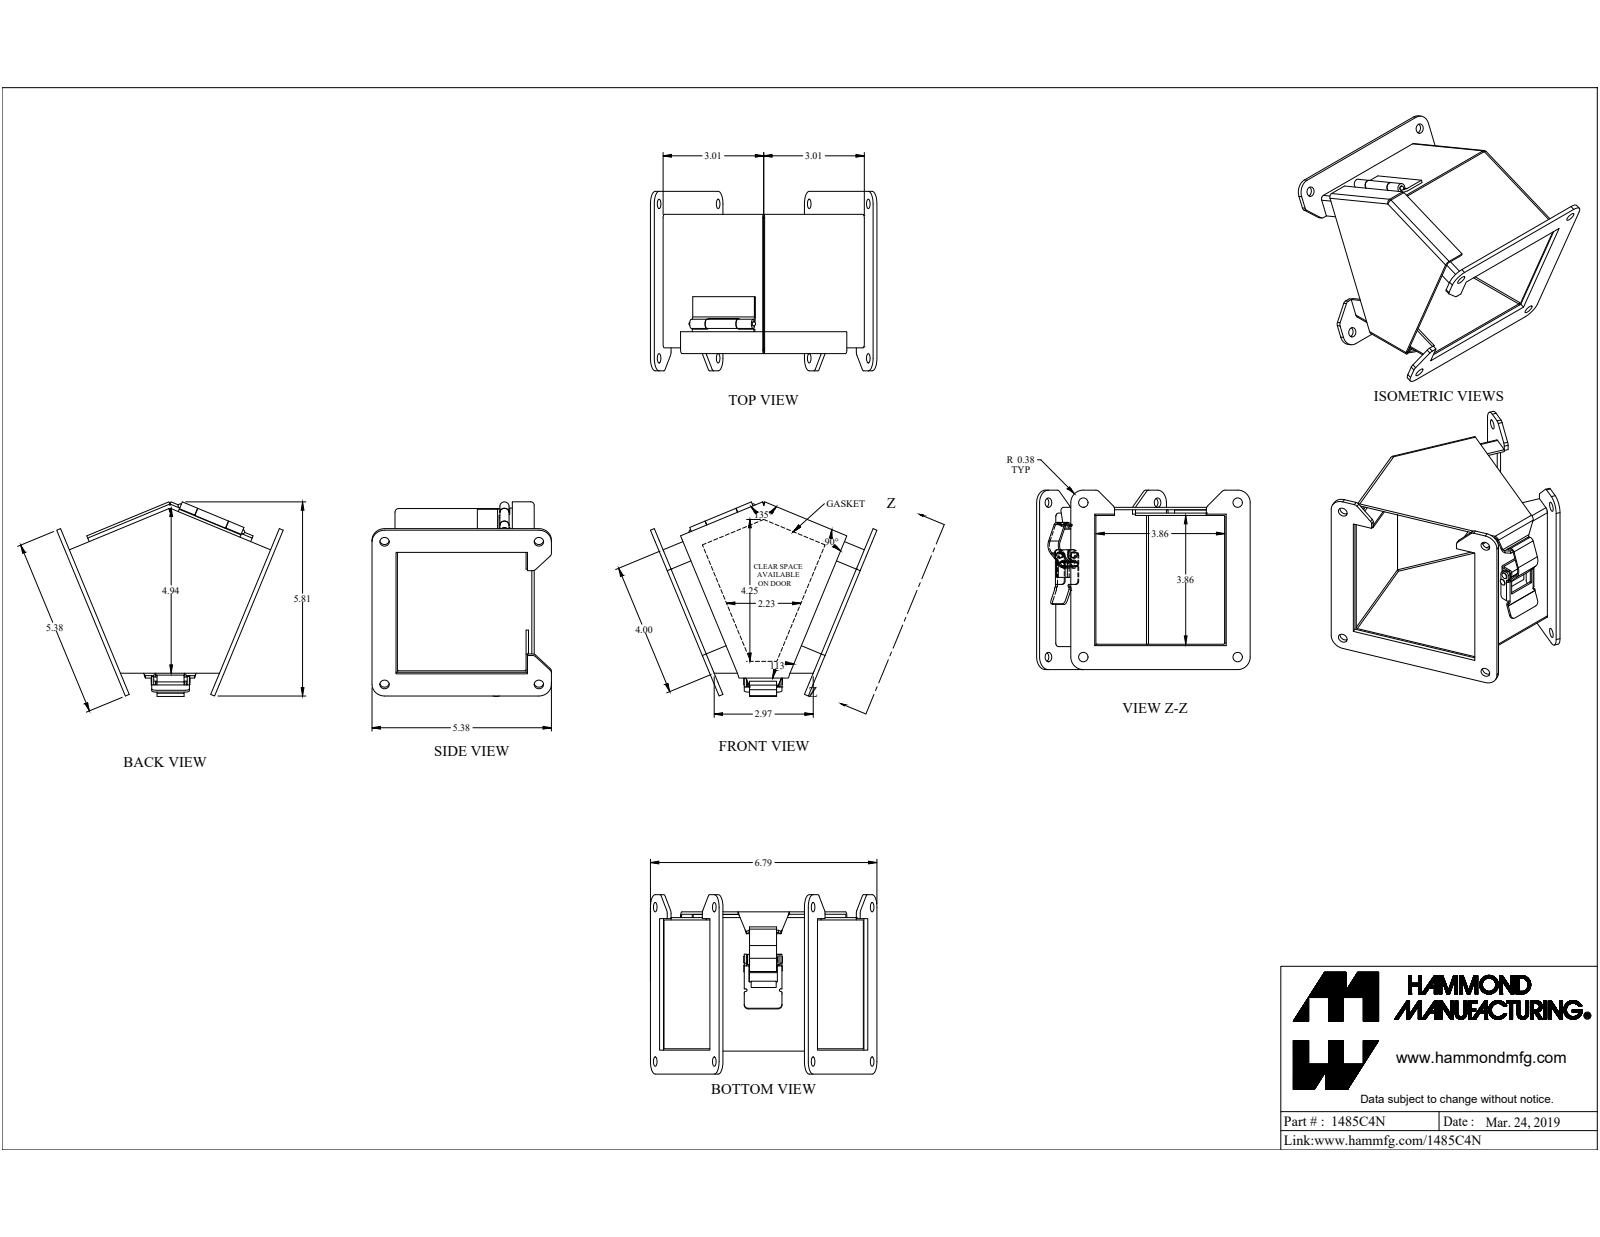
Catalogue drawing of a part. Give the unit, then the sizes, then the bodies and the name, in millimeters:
Units: millimetres
Overall size (bounding box): 172.4 × 148.1 × 136.5
Round holes (diameter × count): ⌀7.1 ×8, ⌀3.2 ×2, ⌀3.3 ×1, ⌀4.2 ×1
Round bosses / shafts (diameter × count): ⌀4.7 ×2, ⌀7 ×1, ⌀7 ×1, ⌀4 ×1, ⌀3.2 ×1, ⌀3.2 ×1
Partial cylindrical surfaces — rounded edges, fillets, slot ends (radius × count): R3.2 ×11, R0.9 ×10, R2.7 ×10, R9.5 ×8, R0.4 ×7, R0.9 ×3, R1 ×3, R1.9 ×3
Main face-to-face distances: 1.8, 104.1, 3.2, 102.3, 106, 4.4, 99.8, 6.2, 97.9, 2.5
Hole centre spacings: 117.5, 166.1, 26.4, 91.3, 7.2, 117, 117, 146.1
Volume: 151 600 mm³ · Surface area: 156 900 mm²
Bodies: 10 solids, 280 faces (165 planar, 103 cylindrical, 12 other)
Part name (STEP PRODUCT): 1485C4N
STEP written by: SolidWorks 2019 (CONFIG_CONTROL_DESIGN)
